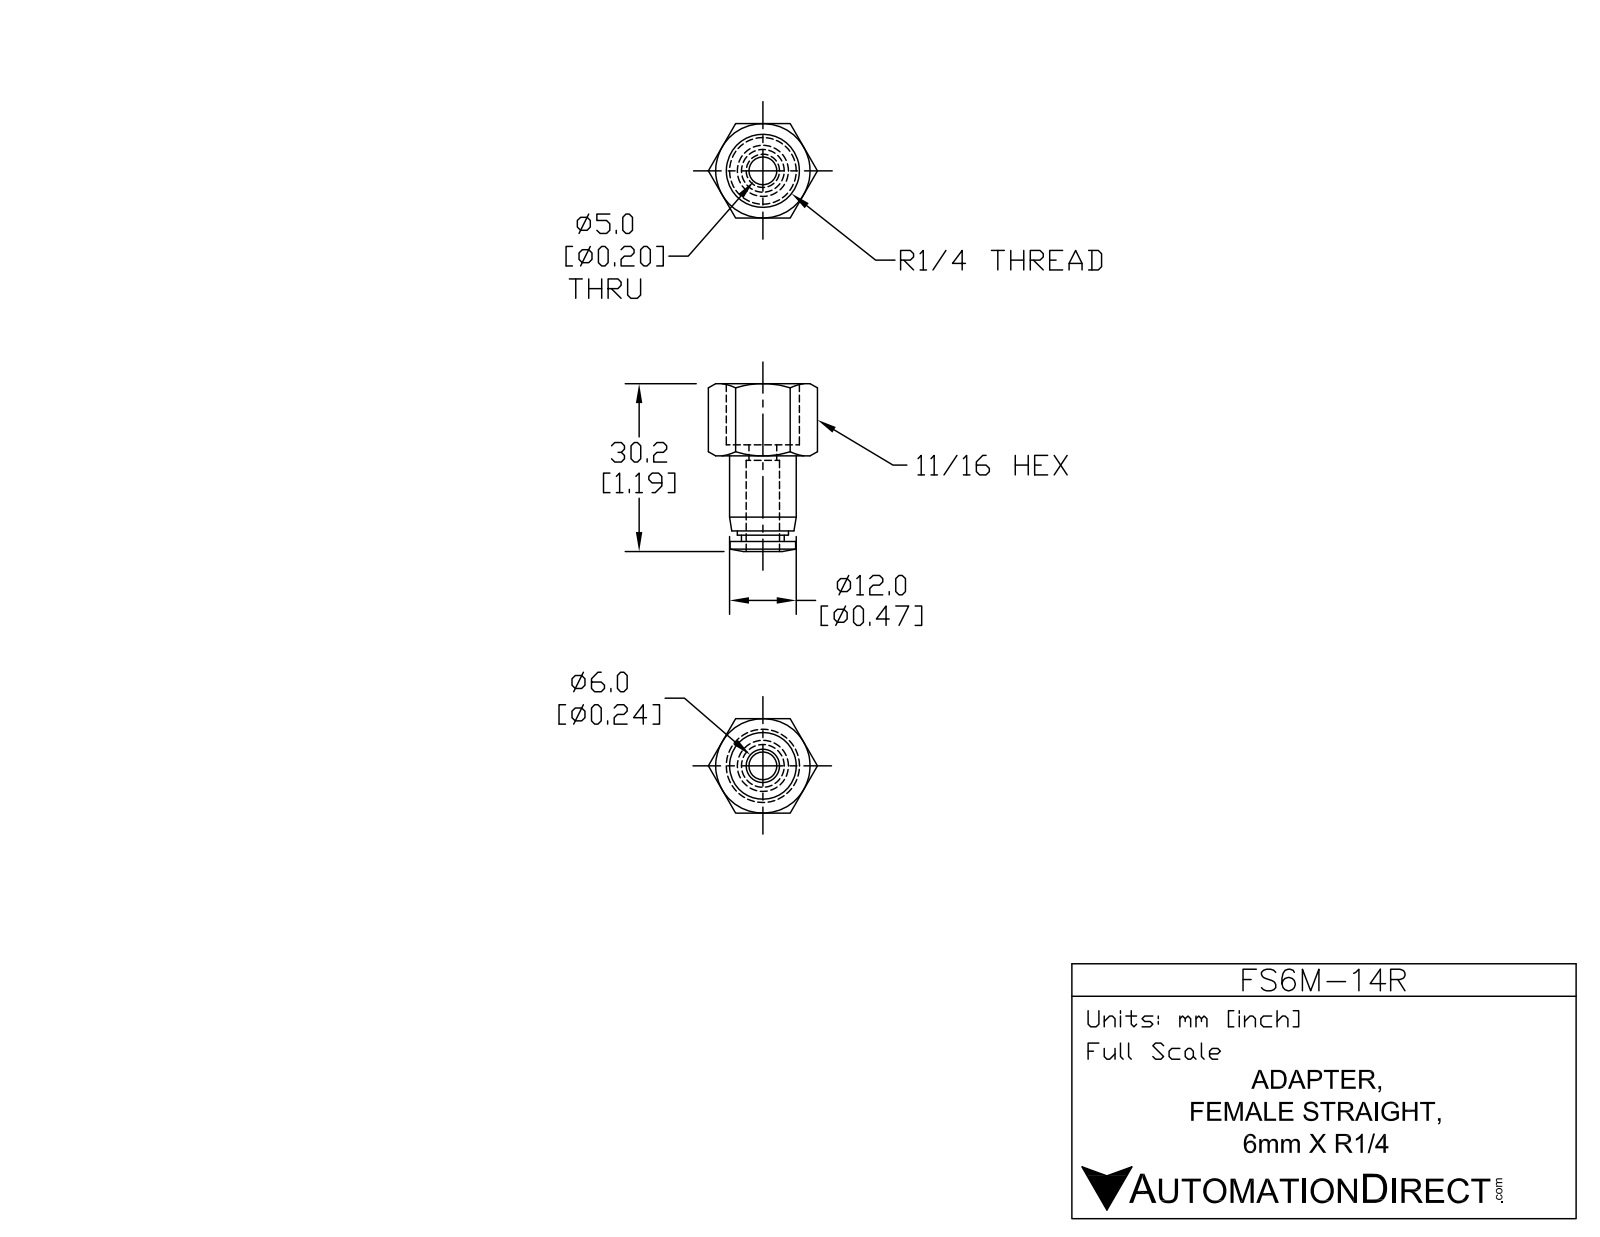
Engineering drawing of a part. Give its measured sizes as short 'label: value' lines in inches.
name: FS6M-14R
written by: SolidWorks 2015 (AUTOMOTIVE_DESIGN)
unit: in
bodies: 1 solid, 48 faces (14 planar, 12 cylindrical, 22 other)
size: 1.189 × 0.773 × 0.669
volume: 0.186 in³; area: 4.214 in²
holes: 1× ⌀0.197, 1× ⌀0.248
bosses: 1× ⌀0.472, 1× ⌀0.465, 1× ⌀0.362, 1× ⌀0.303
face distances: 0.669, 0.079, 0.433, 0.512, 1.118, 0.685, 0.606, 1.043, 0.61, 0.531
